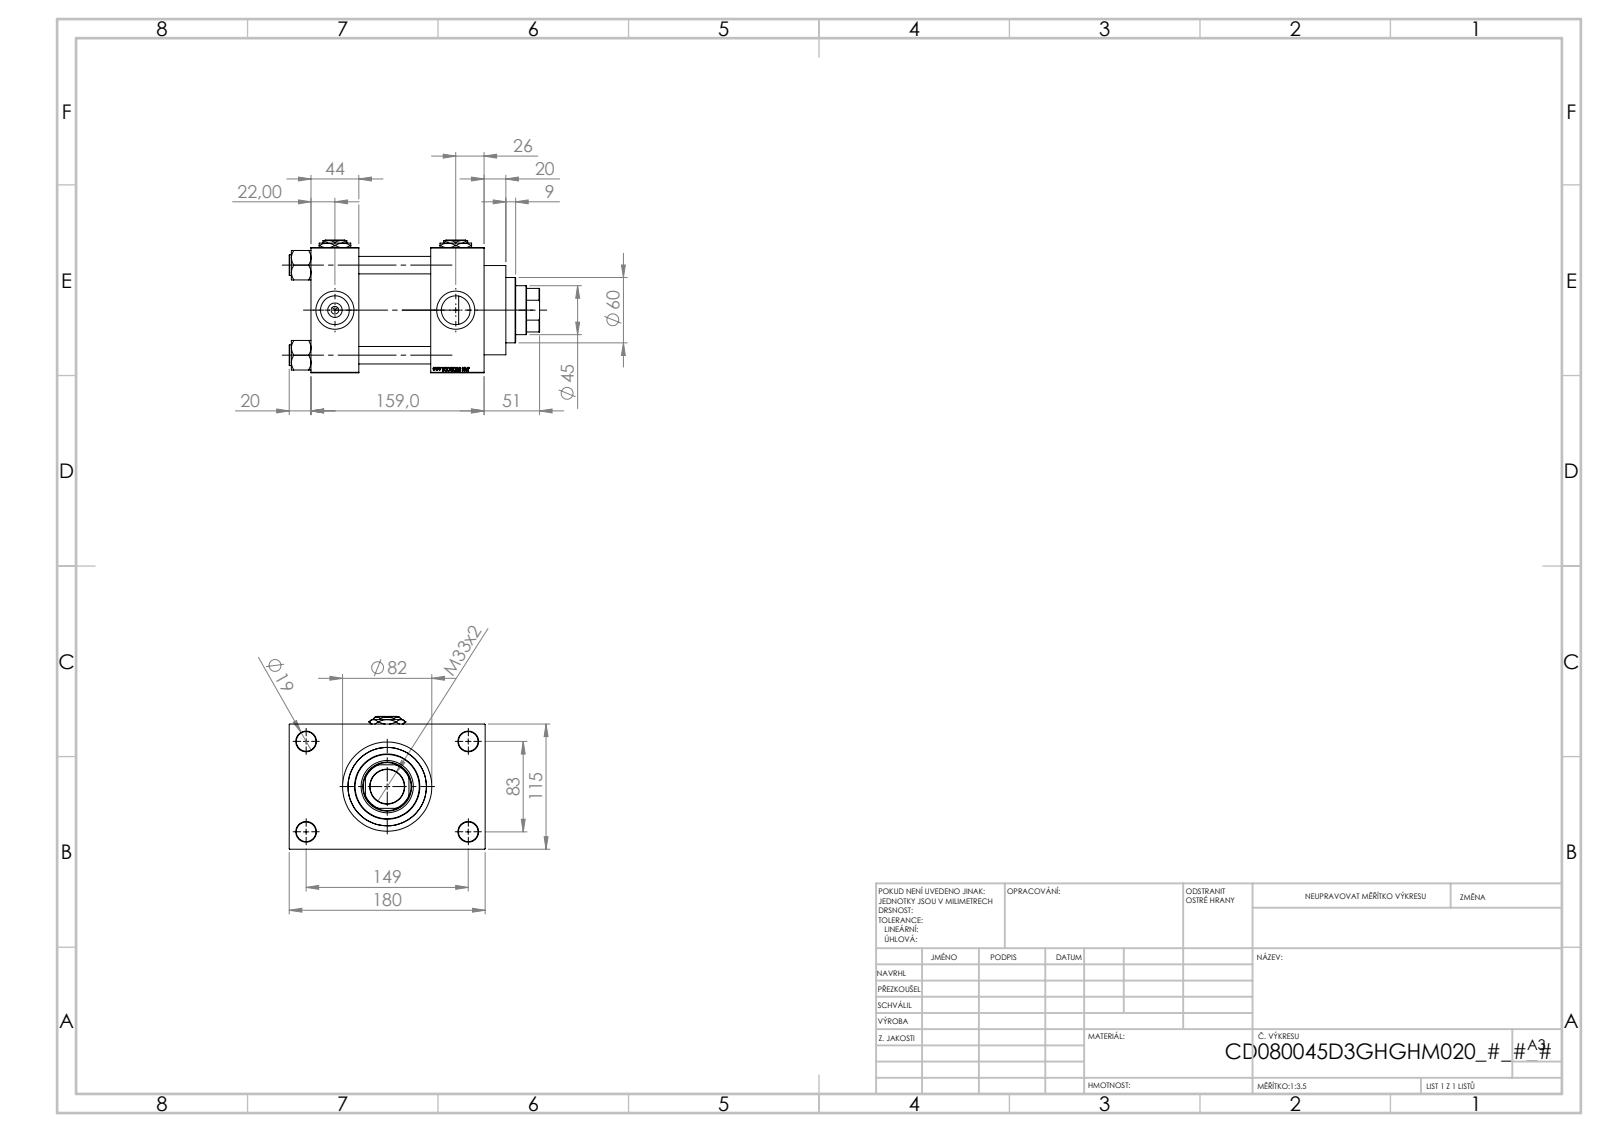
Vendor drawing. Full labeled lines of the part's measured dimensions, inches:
Part name (STEP PRODUCT): V215CD_VCP_D; V215CD_VC_A; Zatka_pro_OIL_PORT; V215CD_NUT_M5_D (+2 more)
STEP written by: SolidWorks 2019 (CONFIG_CONTROL_DESIGN)
Units: inches
Bodies: 13 solids, 1252 faces (593 planar, 99 cylindrical, 560 other)
Overall size (bounding box): 9.055 × 7.087 × 4.803
Volume: 121.4 in³ · Surface area: 479.2 in²
Round holes (diameter × count): ⌀0.63 ×4, ⌀0.709 ×4, ⌀1.041 ×4, ⌀1.378 ×4, ⌀0.276 ×3, ⌀1.24 ×1, ⌀1.772 ×1, ⌀1.89 ×1, ⌀2.402 ×1, ⌀2.835 ×1, ⌀3.15 ×1
Round bosses / shafts (diameter × count): ⌀0.748 ×4, ⌀3.386 ×1, ⌀3.228 ×1, ⌀2.362 ×1
Partial cylindrical surfaces — rounded edges, fillets, slot ends (radius × count): R0.866 ×1
Main face-to-face distances: 4.528, 4.331, 2.598, 1.929, 1.732, 6.26, 1.28, 5.807, 0.787, 2.717
Hole centre spacings: 1.305, 2.302, 3.256, 3.357, 3.513, 4.561, 5.607, 3.268
